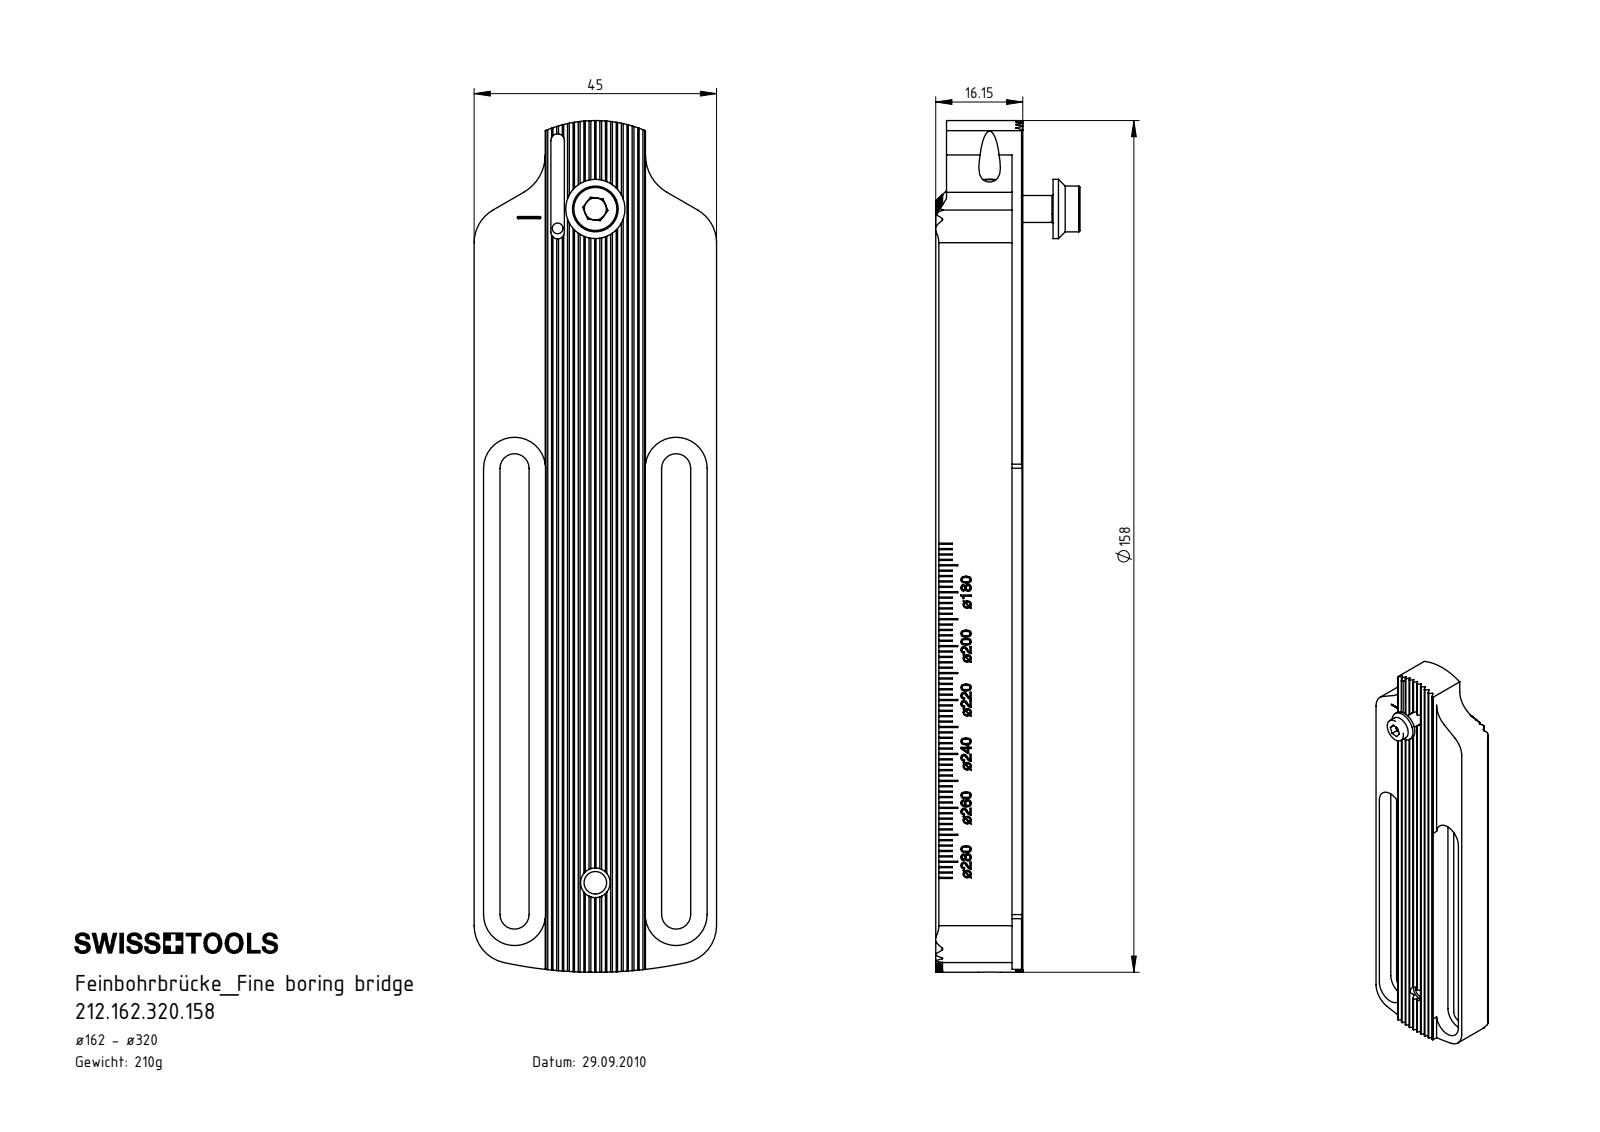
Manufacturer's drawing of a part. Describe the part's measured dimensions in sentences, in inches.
The part is named "MH1-BV2.K02.015_B; KVT_MB_600_040; ISO 4026 - M4 x 5; MH1.BV2.K02.015 (+1 more)". Its 3-D file was written by "SolidWorks 2017 (AUTOMOTIVE_DESIGN)". It is 8 solids with 1158 faces: 708 planar, 149 cylindrical and 301 other. Overall it measures 6.22 by 1.772 by 1.054 inches. Its volume is 4.456 cubic inches and its surface area 49.08 square inches. Round holes: 6 of diameter 0.165, 5 of diameter 0.13, 2 of diameter 0.217, 1 of diameter 0.079, 1 of diameter 0.118. Round bosses or shafts: 5 of diameter 0.157, 1 of diameter 0.433, 1 of diameter 0.335, 1 of diameter 0.197. Partial cylindrical surfaces (rounded edges, fillets, slot ends): 31 of radius 0.006, 4 of radius 0.106, 4 of radius 0.226, 4 of radius 0.276, 2 of radius 0.049, 2 of radius 0.315, 1 of radius 0.945, 1 of radius 3.189. The main face-to-face distances are 0.068, 0.136, 0.341, 0.273, 0.636, 0.205, 0.227, 1.181, 0.12, 0.333. The hole center spacings are 0.787, 0.31, 0.843, 1.575, 1.63, 2.378, 2.417, 2.504.
